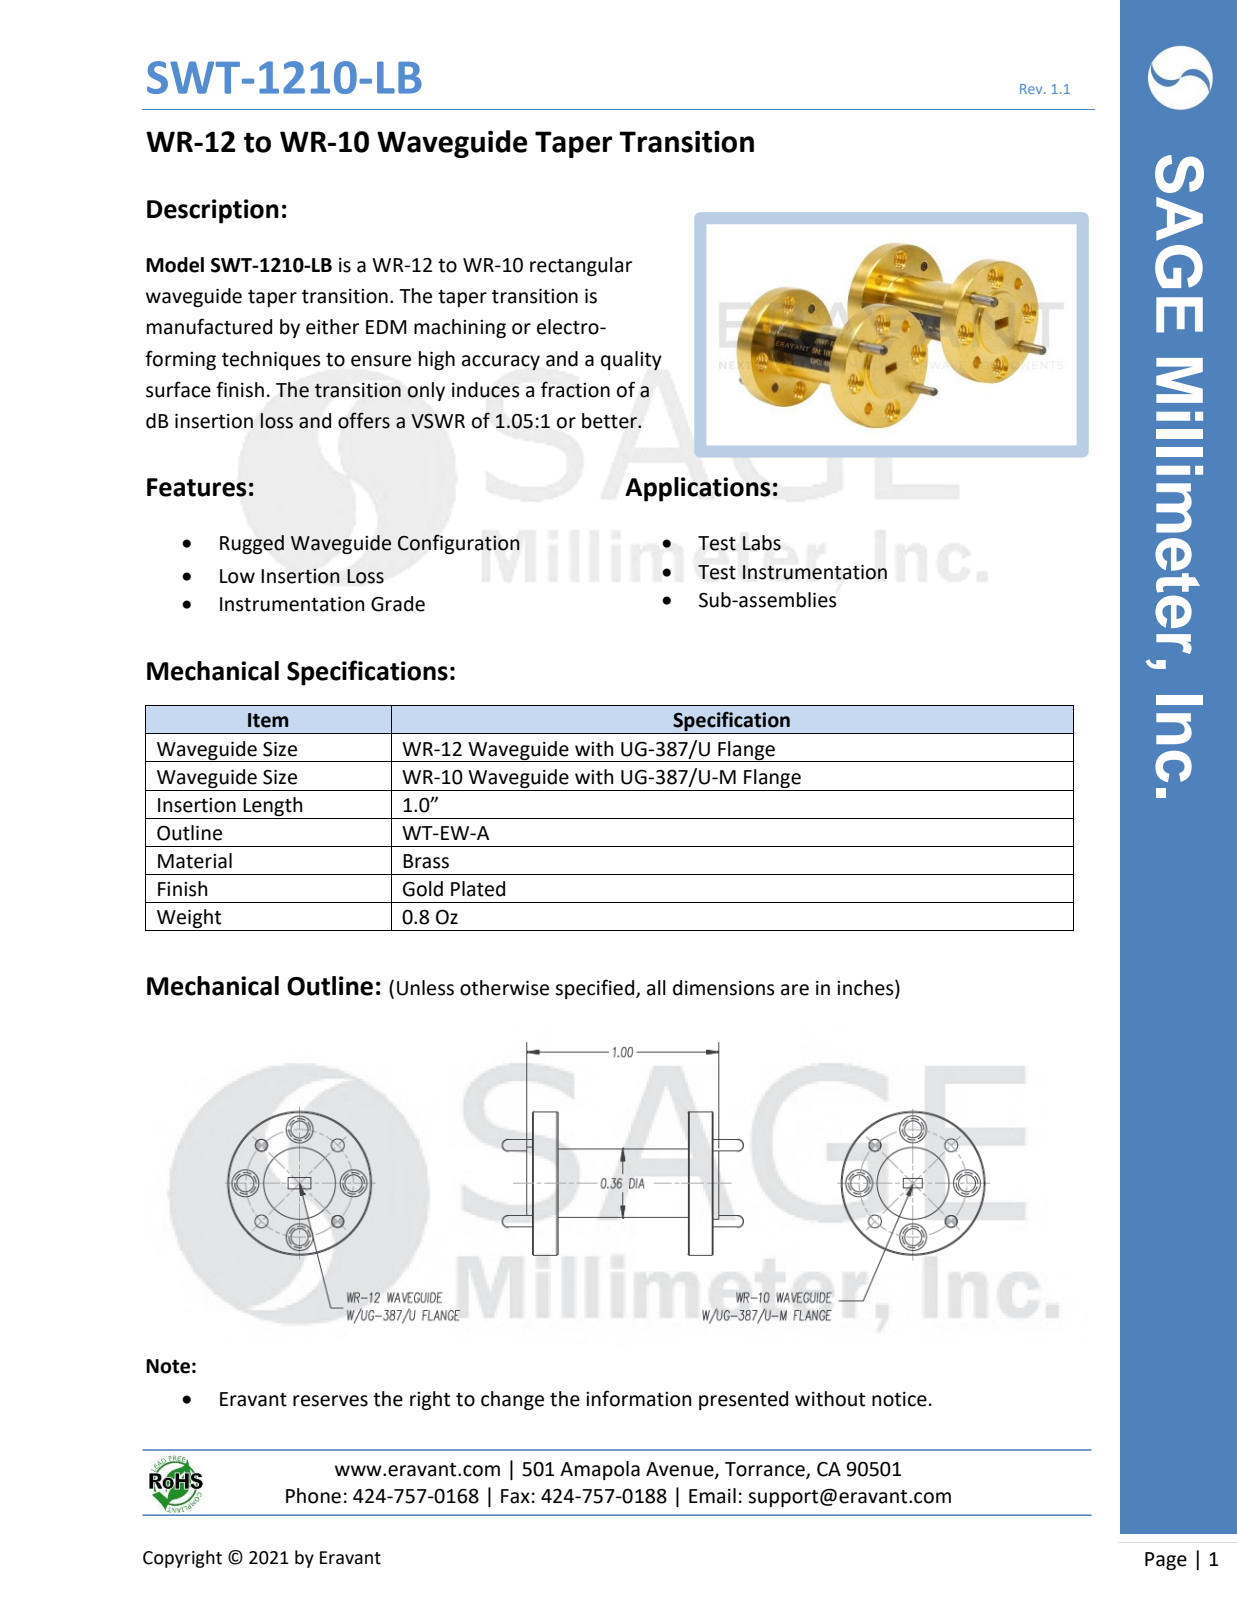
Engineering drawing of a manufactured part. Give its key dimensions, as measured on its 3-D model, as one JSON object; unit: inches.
{"part_name": "SWT-1210-LB", "step_written_by": "SolidWorks 2013 (CONFIG_CONTROL_DESIGN)", "units": "inches", "bodies": {"solids": 0, "faces": 130, "planar": 24, "cylindrical": 66, "other": 40}, "overall_size": [1.305, 0.75, 0.75], "round_holes": [[0.06, 4], [0.067, 4], [0.089, 4], [0.151, 4]], "round_bosses_or_shafts": [[0.063, 4], [0.75, 1], [0.375, 1], [0.36, 1]], "face_to_face_distances": [0.68, 0.03, 0.97, 0.81, 0.13, 0.13, 0.81, 0.94, 0.84, 0.16], "hole_center_spacings": [0.215, 0.398, 0.519, 0.562, 0.52, 0.563]}
